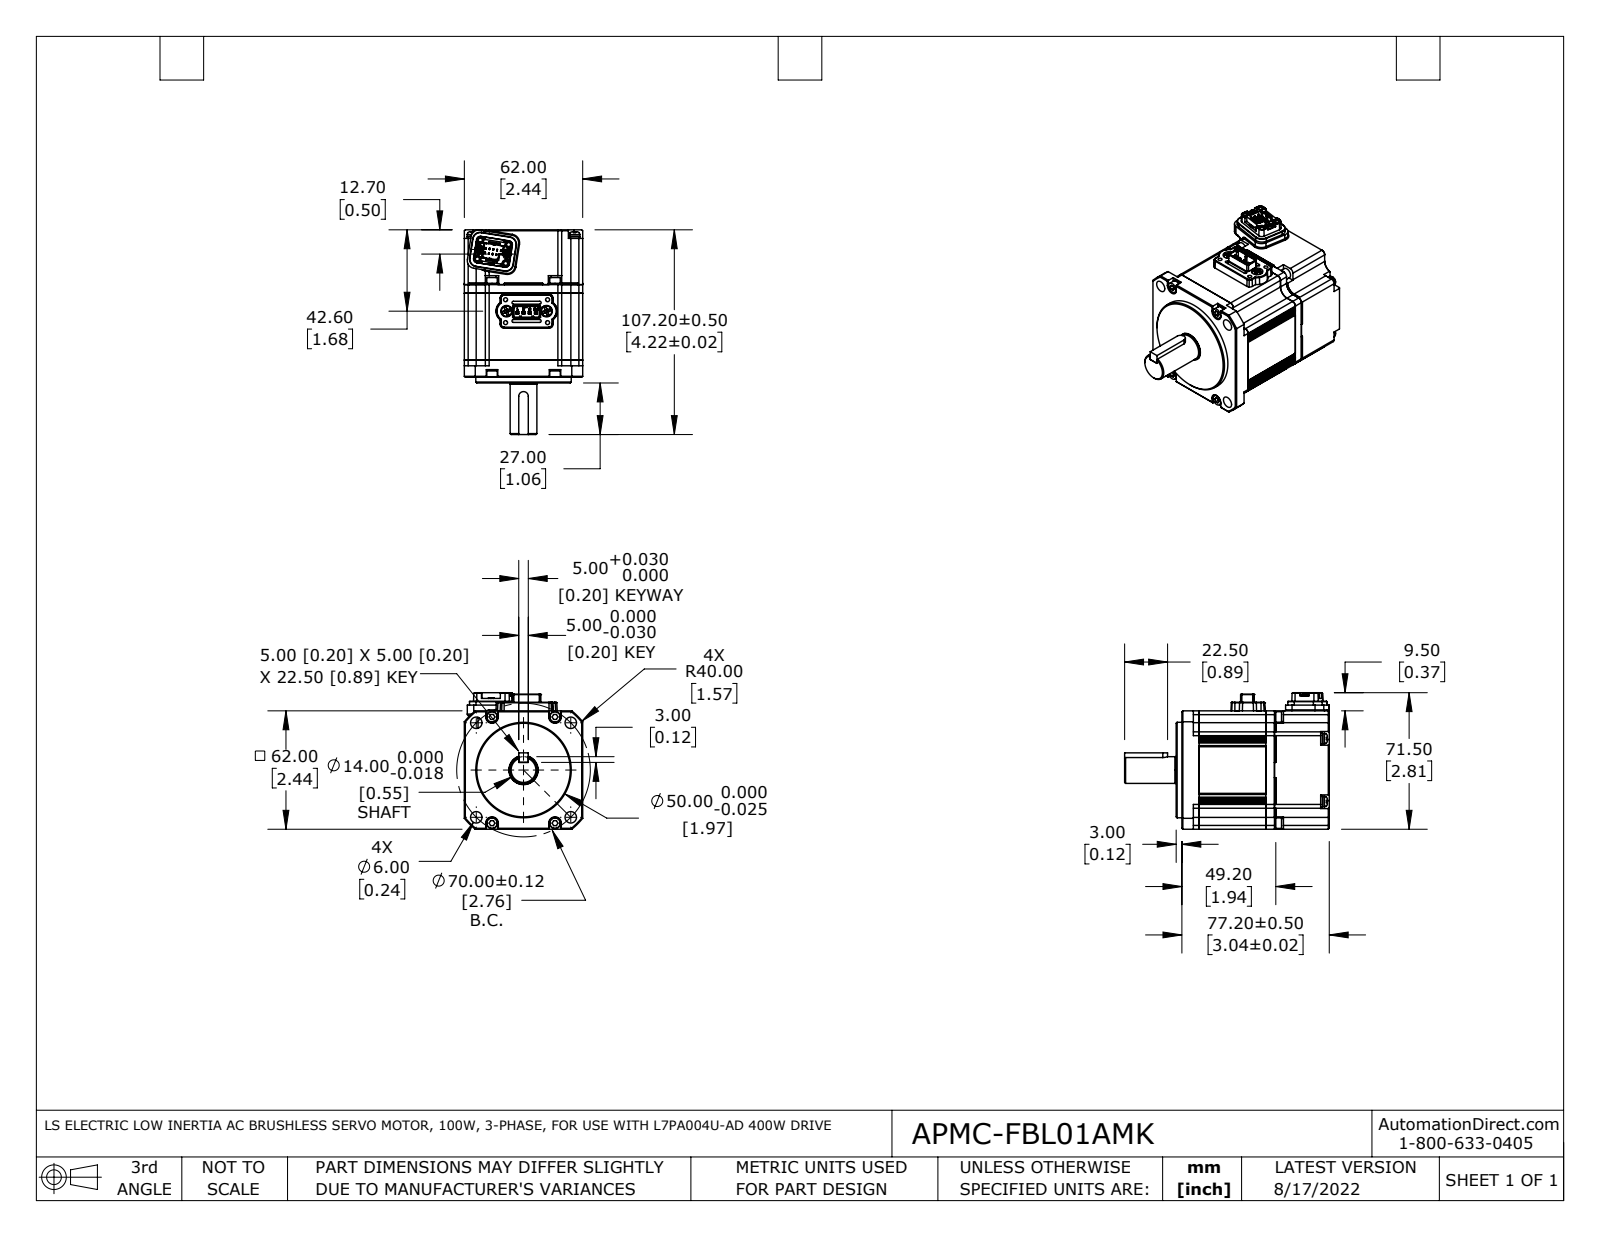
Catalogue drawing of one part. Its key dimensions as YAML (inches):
part_name: "SLM06GA001G01_Out Line(APMC-FBL01AMK) r1 nc fxt"
step_written_by: "SolidWorks 2017 (AUTOMOTIVE_DESIGN)"
units: inches
bodies: {solids: 45, faces: 1837, planar: 1167, cylindrical: 488, other: 182}
overall_size: [4.22, 2.815, 2.441]
volume: 16.83
surface_area: 106
round_holes:
  - {diameter: 0.083, count: 10}
  - {diameter: 0.118, count: 10}
  - {diameter: 0.138, count: 8}
  - {diameter: 0.236, count: 6}
  - {diameter: 0.122, count: 4}
  - {diameter: 0.079, count: 2}
  - {diameter: 0.13, count: 1}
  - {diameter: 0.134, count: 1}
  - {diameter: 0.602, count: 1}
round_bosses_or_shafts:
  - {diameter: 0.213, count: 6}
  - {diameter: 0.22, count: 4}
  - {diameter: 0.217, count: 4}
  - {diameter: 0.087, count: 2}
  - {diameter: 1.969, count: 1}
  - {diameter: 0.591, count: 1}
  - {diameter: 0.583, count: 1}
  - {diameter: 0.551, count: 1}
partial_cylinders:
  - {radius: 0.008, count: 20}
  - {radius: 0.012, count: 20}
  - {radius: 0.039, count: 12}
  - {radius: 0.006, count: 9}
  - {radius: 0.079, count: 8}
  - {radius: 0.118, count: 8}
  - {radius: 0.018, count: 7}
  - {radius: 0.004, count: 6}
face_to_face_distances: [0.177, 1.378, 0.028, 1.555, 0.205, 1.583, 2.441, 0.118, 1.13, 1.102]
hole_center_spacings: [1.762, 0.237, 0.335, 0.346, 0.602, 0.63, 0.879, 1.239]
